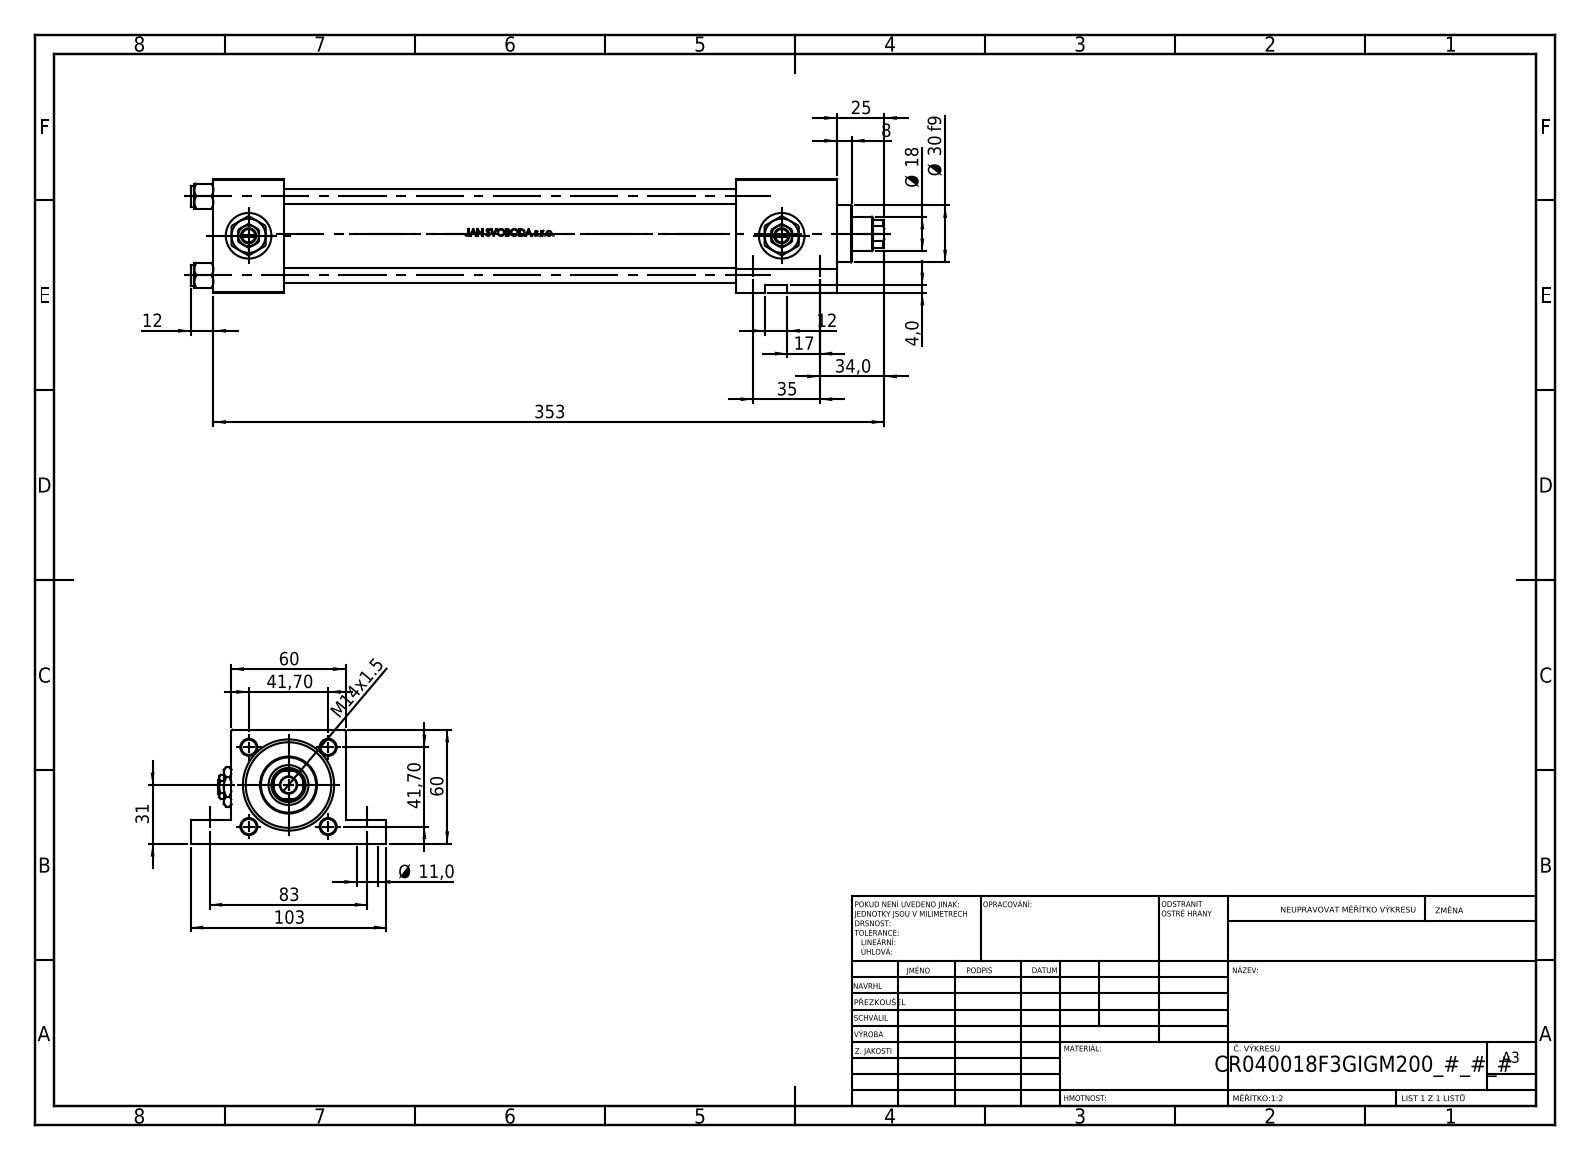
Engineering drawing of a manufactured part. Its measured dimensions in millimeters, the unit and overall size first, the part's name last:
Units: millimetres
Overall size (bounding box): 365 × 103 × 60
Round holes (diameter × count): ⌀8 ×4, ⌀11 ×4, ⌀16.66 ×3, ⌀24 ×3, ⌀7 ×2, ⌀8.5 ×1, ⌀16 ×1, ⌀18 ×1, ⌀21 ×1, ⌀31 ×1, ⌀40 ×1, ⌀45 ×1
Round bosses / shafts (diameter × count): ⌀11 ×4, ⌀46 ×1, ⌀30 ×1
Partial cylindrical surfaces — rounded edges, fillets, slot ends (radius × count): R8.5 ×1
Main face-to-face distances: 60, 37, 328, 291, 275, 238, 53, 299.3, 262.3, 24.3
Hole centre spacings: 41.7, 28.79, 30.2, 35, 42.09, 50.06, 58.97, 83
Volume: 575 317 mm³ · Surface area: 191 375 mm²
Bodies: 13 solids, 1215 faces (484 planar, 149 cylindrical, 582 other)
Part name (STEP PRODUCT): V215CR_F_Body; NUT_M5_F; Zatka_pro_OIL_PORT; V215CR_VCP_F (+2 more)
STEP written by: SolidWorks 2019 (CONFIG_CONTROL_DESIGN)
